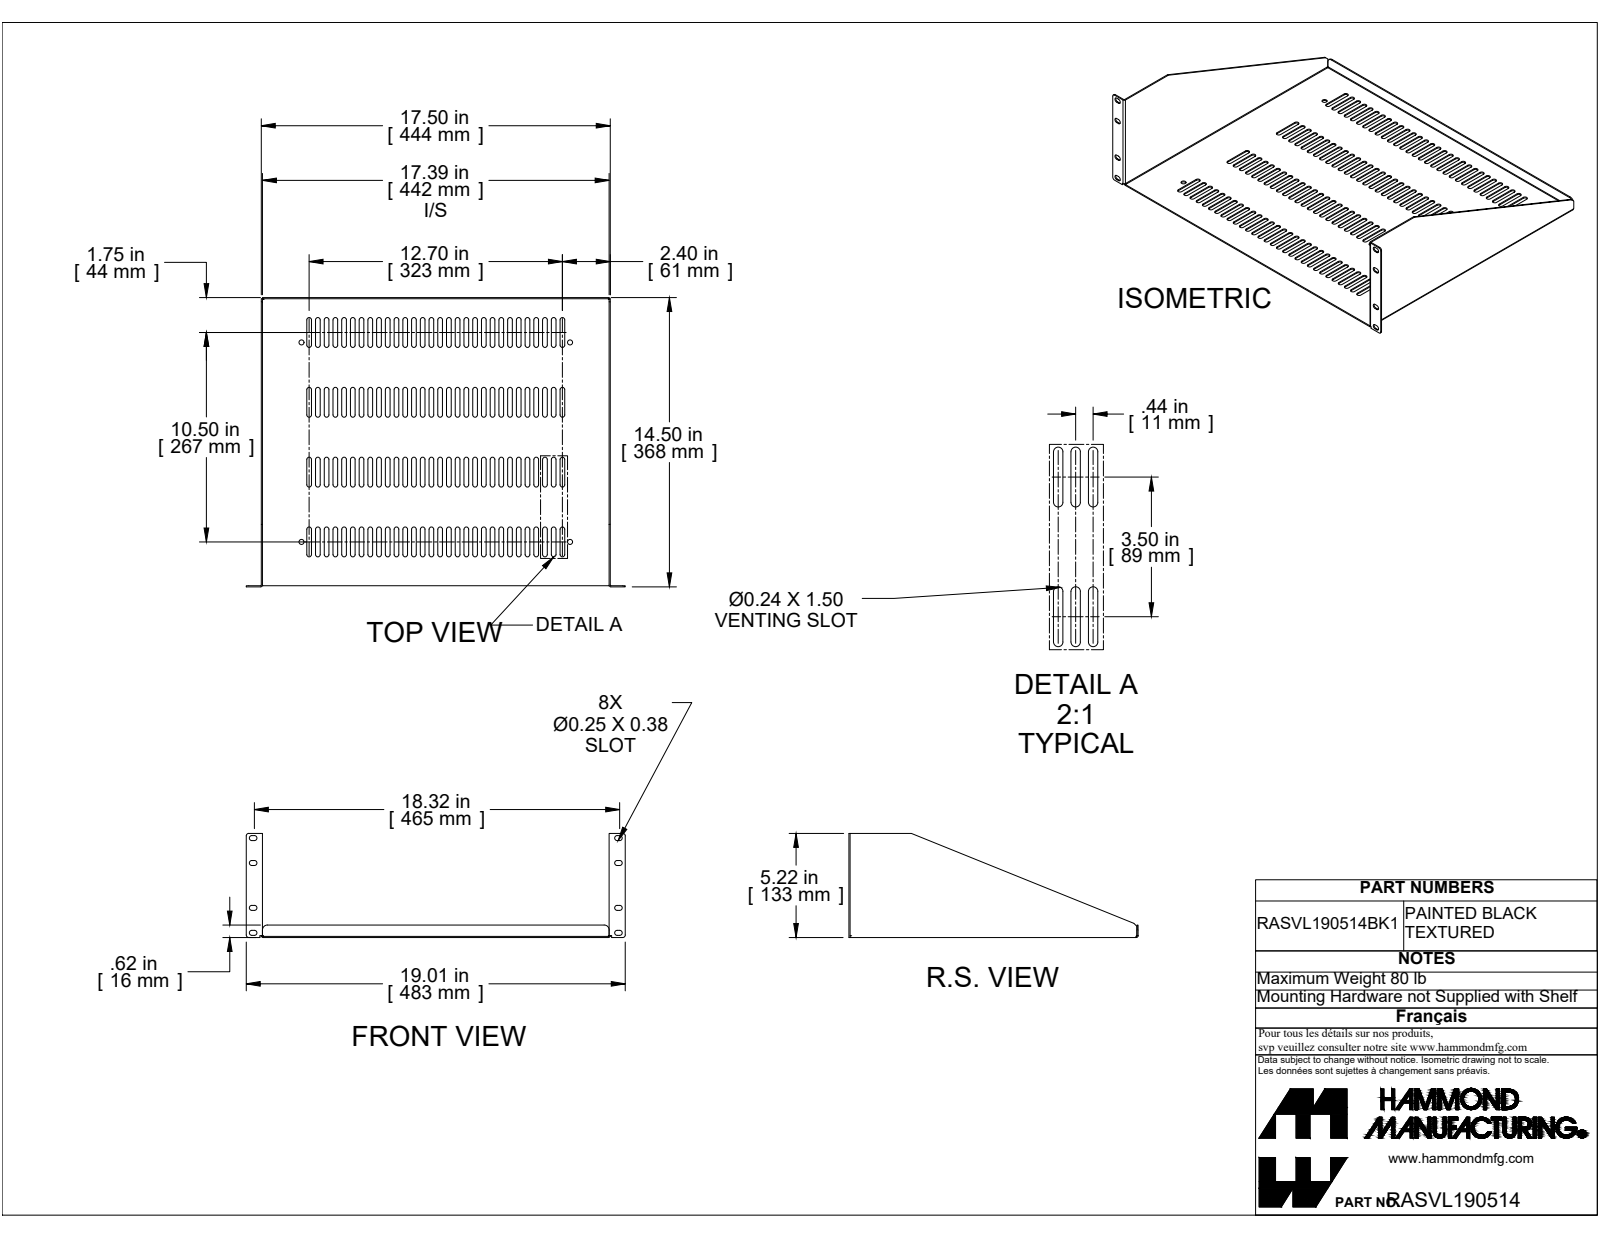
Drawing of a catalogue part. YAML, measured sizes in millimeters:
part_name: "RASVL190514BK1"
step_written_by: "SolidWorks 2019 (CONFIG_CONTROL_DESIGN)"
units: millimeters
bodies: {solids: 0, faces: 582, planar: 298, cylindrical: 280, other: 4}
overall_size: [482.8, 368.3, 132.5]
round_bosses_or_shafts:
  - {diameter: 6.4, count: 4}
partial_cylinders:
  - {radius: 3, count: 228}
  - {radius: 3.2, count: 20}
  - {radius: 3, count: 12}
  - {radius: 0.7, count: 5}
  - {radius: 2.2, count: 5}
  - {radius: 1.4, count: 3}
  - {radius: 6.4, count: 2}
face_to_face_distances: [1.4, 443.1, 441.6, 444.5, 365.4, 366.9, 1.4, 366.9, 368.3, 22.3]
